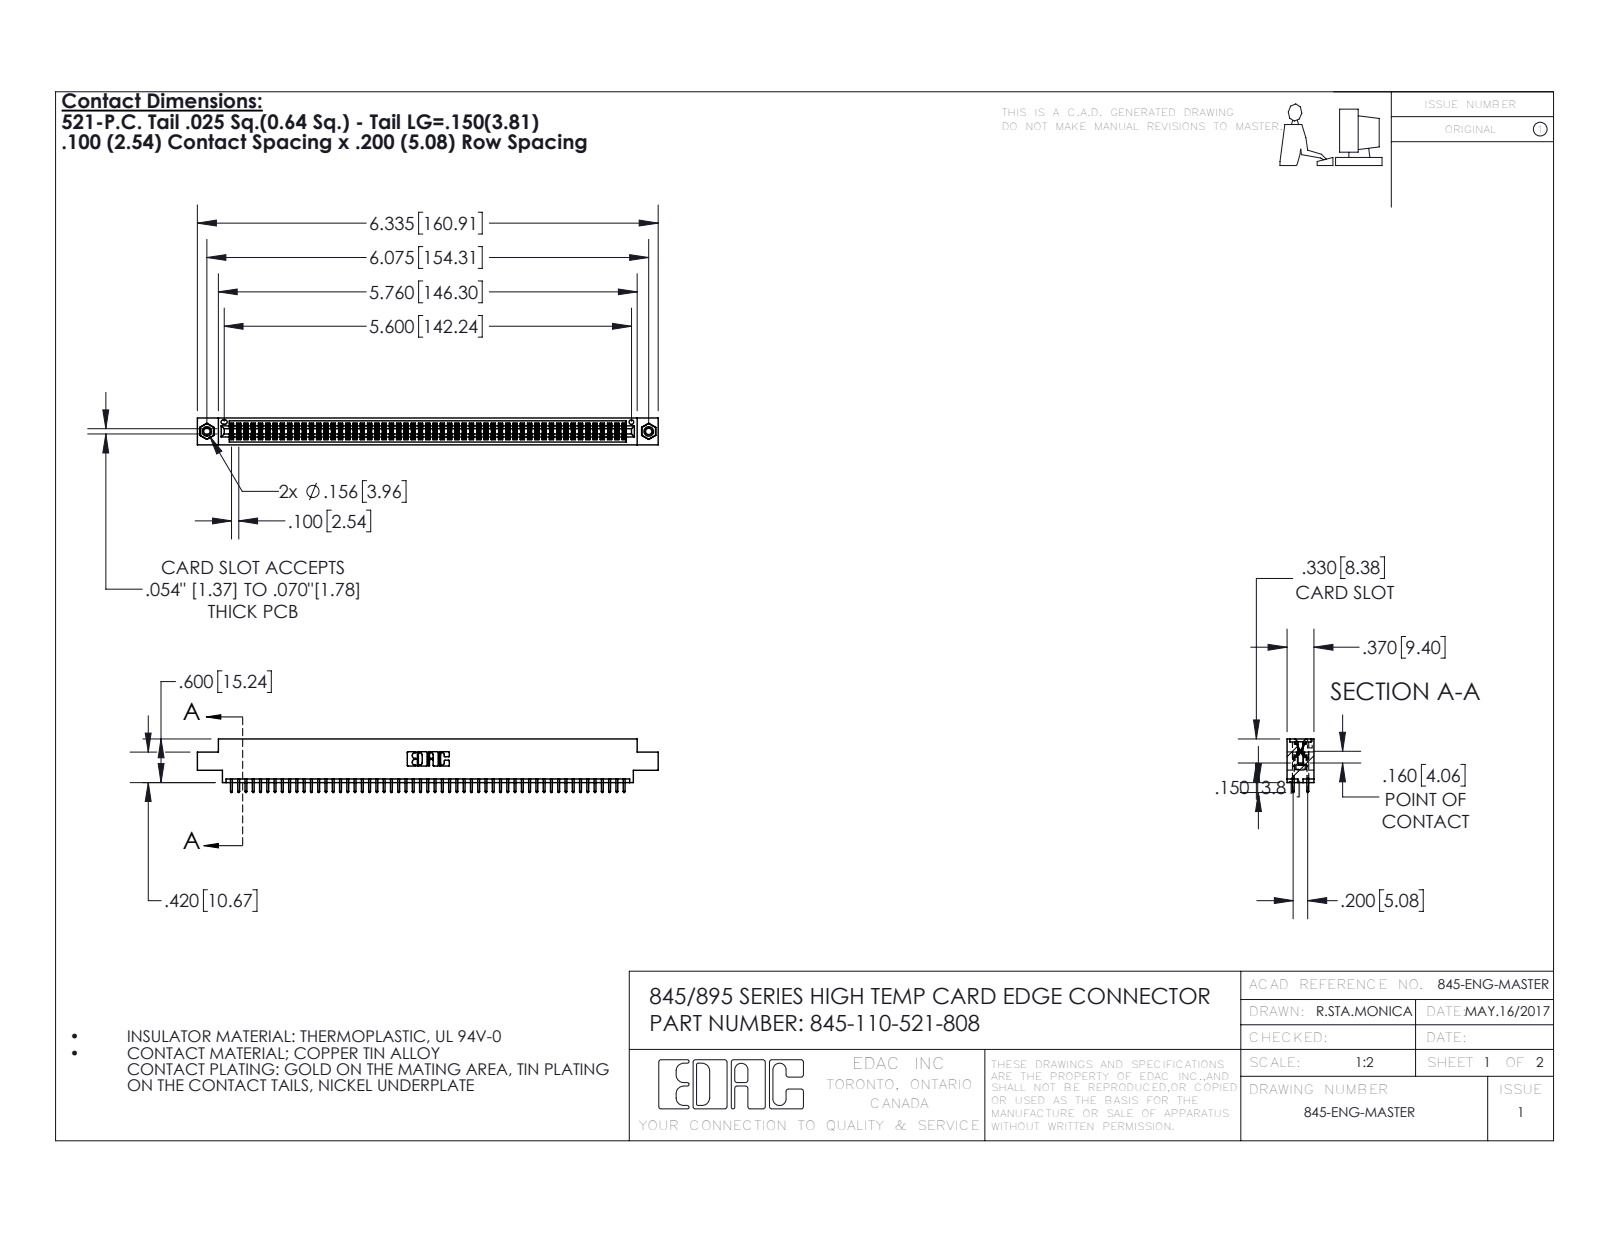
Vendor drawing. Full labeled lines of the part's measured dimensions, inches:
Part name (STEP PRODUCT): 345 Part_0.170 Offset - 0.156 Dia-TI; 345-250-001_345-250-003-102; 345-292-001_345-293-121; 345-110-521-808
STEP written by: SolidWorks 2016 (CONFIG_CONTROL_DESIGN)
Units: inches
Bodies: 113 solids, 5690 faces (3746 planar, 1928 cylindrical, 16 other)
Overall size (bounding box): 6.335 × 0.737 × 0.37
Volume: 0.951 in³ · Surface area: 35.89 in²
Round holes (diameter × count): ⌀0.089 ×2, ⌀0.125 ×2, ⌀0.156 ×2, ⌀0.064 ×1
Round bosses / shafts (diameter × count): ⌀0.155 ×2
Partial cylindrical surfaces — rounded edges, fillets, slot ends (radius × count): R0.006 ×166, R0.01 ×110, R0.01 ×22, R0.007 ×6, R0.031 ×6, R0.026 ×3, R0.014 ×2, R0.019 ×2
Main face-to-face distances: 0.072, 0.298, 0.2, 0.37, 0.098, 0.272, 0.025, 0.225, 0.175, 0.149
Hole centre spacings: 0.27, 5.839, 6.075
